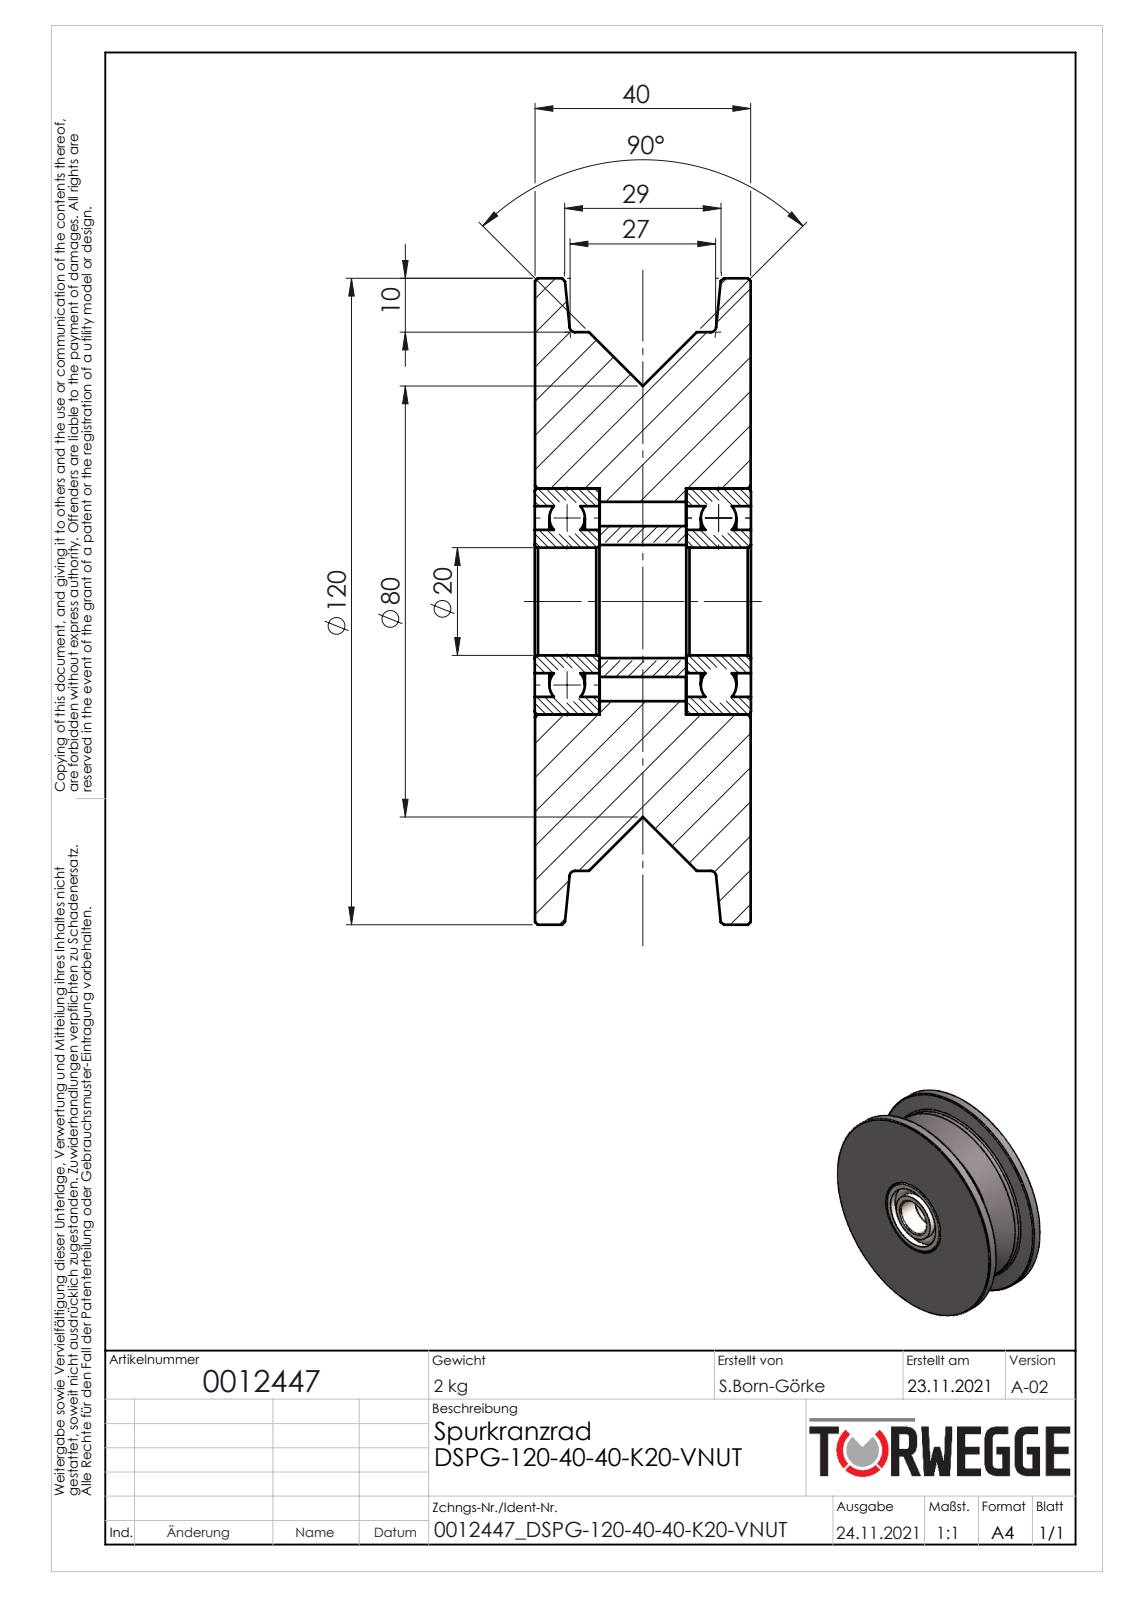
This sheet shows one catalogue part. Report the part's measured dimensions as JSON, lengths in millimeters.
{"part_name": "0012447", "step_written_by": "SolidWorks 2020 (AUTOMOTIVE_DESIGN)", "units": "millimeters", "bodies": {"solids": 12, "faces": 140, "planar": 22, "cylindrical": 58, "other": 60}, "overall_size": [120, 120, 40.1], "volume_mm3": 300789, "surface_area_mm2": 68898, "round_holes": [[20, 1], [22, 1], [26.6, 1], [35.4, 1], [37, 1], [42, 1]], "round_bosses_or_shafts": [[120, 1], [100, 1], [28, 1]], "face_to_face_distances": [40, 0.5, 28.1, 11, 28.05, 1, 11.5, 10.5, 27.6, 28.6]}
